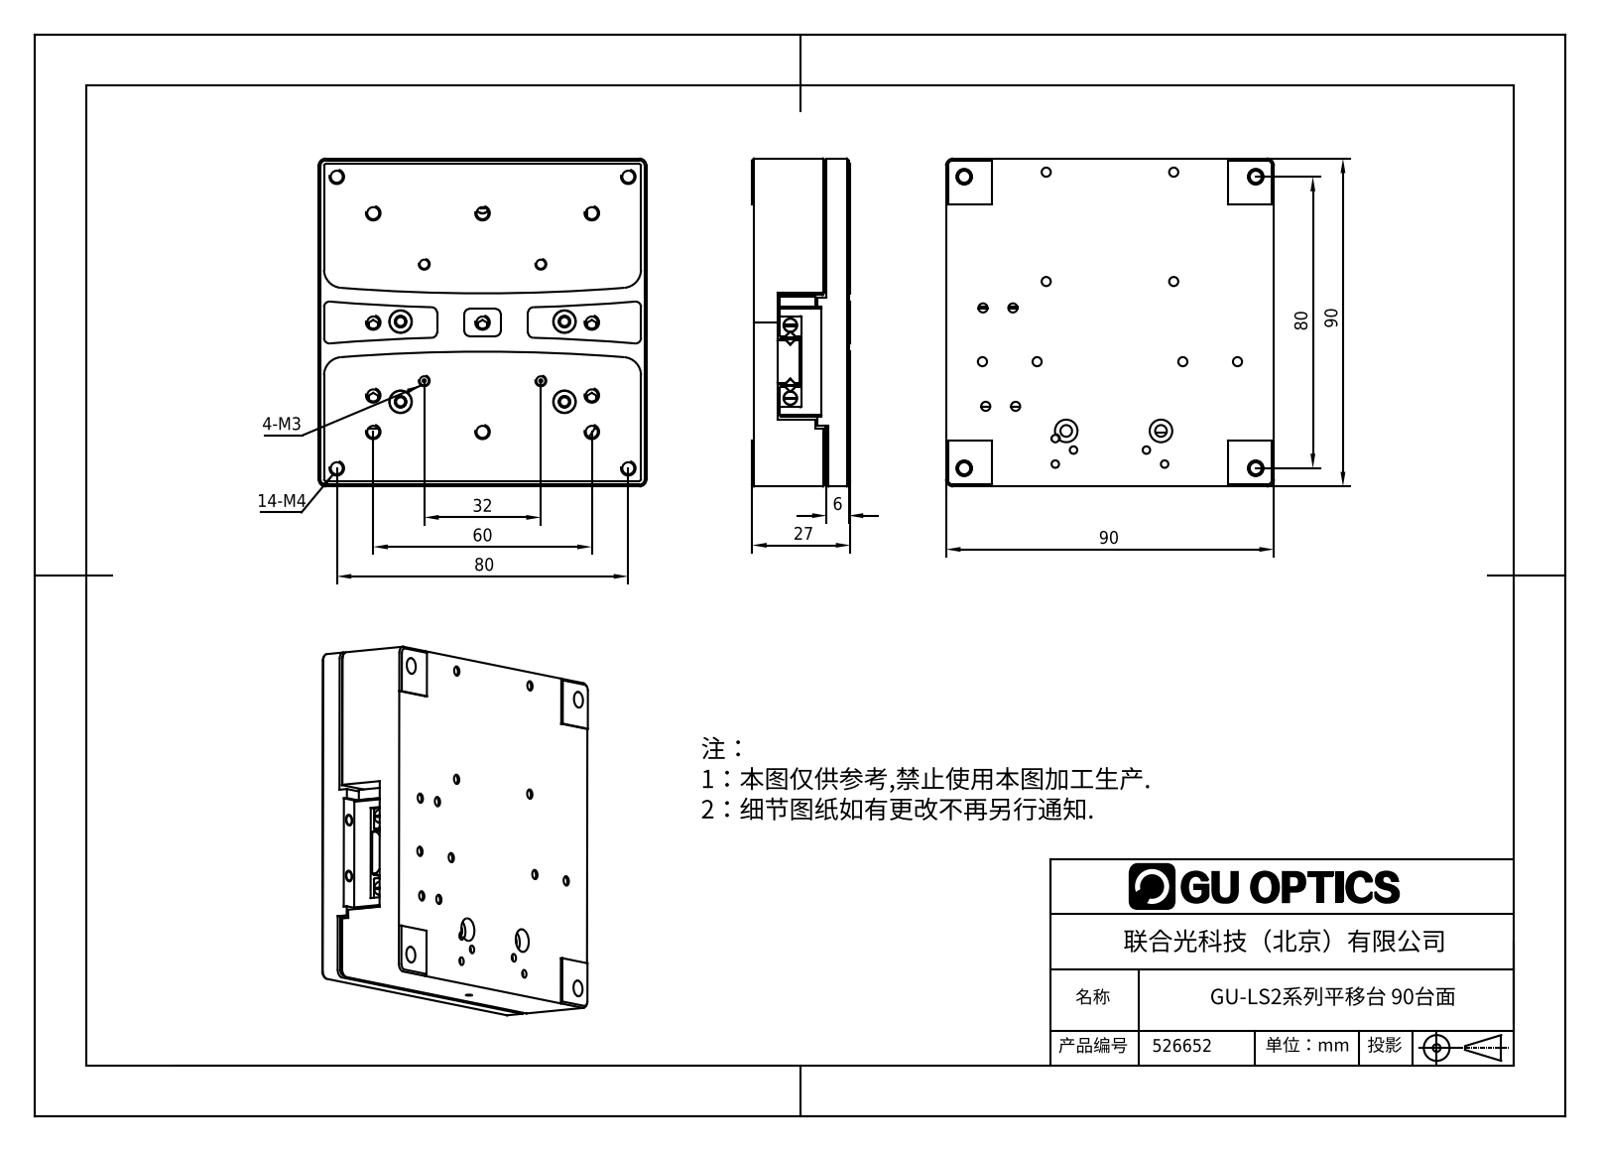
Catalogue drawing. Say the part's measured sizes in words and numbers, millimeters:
The part is named "GU-LS2系列平移台 90台面". Its 3-D file was written by "SolidWorks 2016 (CONFIG_CONTROL_DESIGN)". It is 11 solids with 1131 faces: 537 planar, 335 cylindrical and 259 other. Overall it measures 90 by 90 by 27 millimeters. Its volume is 162 553 cubic millimeters and its surface area 67 425 square millimeters. Round holes: 21 of diameter 2.5, 15 of diameter 3.3, 14 of diameter 6, 10 of diameter 4.5, 6 of diameter 3.2, 6 of diameter 6.2, 5 of diameter 1.57, 5 of diameter 2.05, 4 of diameter 2.46, 4 of diameter 3.5, 4 of diameter 4.3, 4 of diameter 8.25. Round bosses or shafts: 10 of diameter 5.5, 10 of diameter 3, 4 of diameter 7.53, 4 of diameter 4. Partial cylindrical surfaces (rounded edges, fillets, slot ends): 16 of radius 1.5, 12 of radius 3, 9 of radius 2, 7 of radius 0.5, 6 of radius 2.5, 4 of radius 5, 2 of radius 1, 2 of radius 3.2. The main face-to-face distances are 6.5, 20, 0.5, 13.5, 26.5, 7, 13, 6, 1.5, 18.5. The hole center spacings are 15, 30, 7.57, 11.18, 22.3, 22.36, 25, 36.4.
